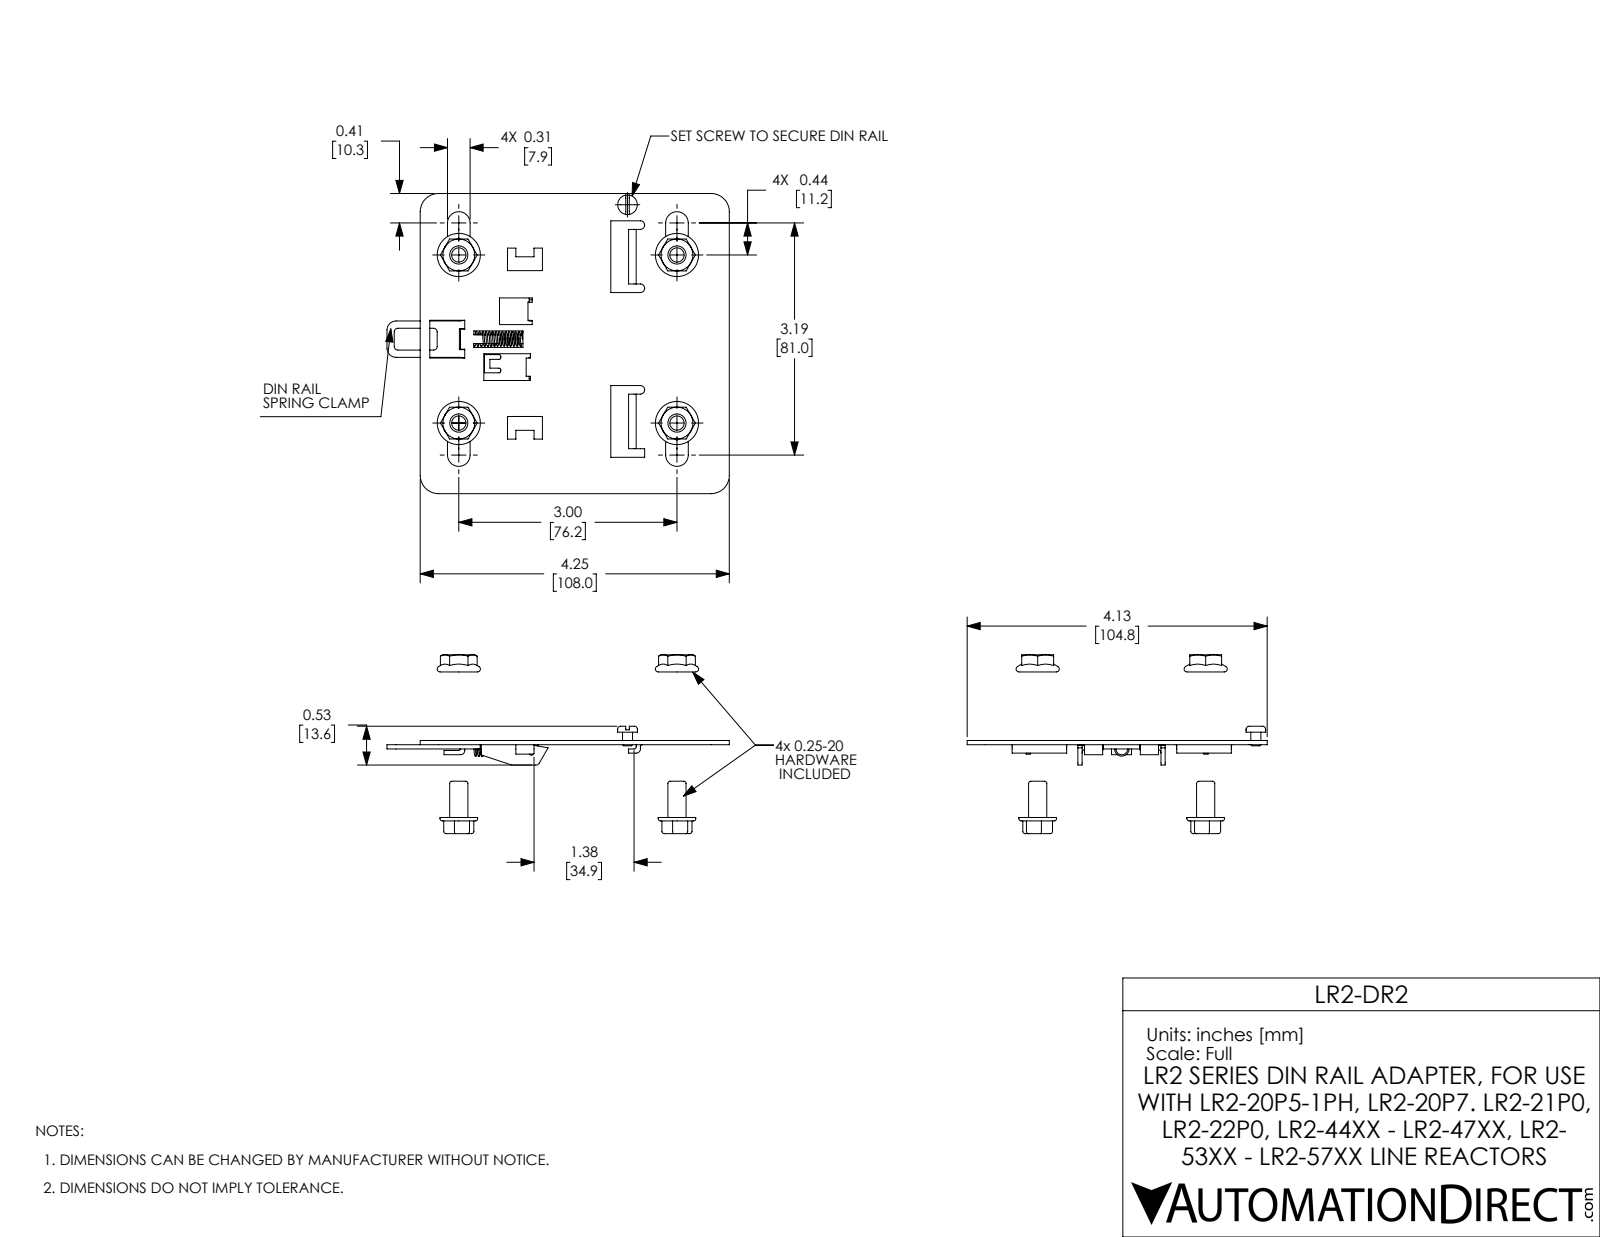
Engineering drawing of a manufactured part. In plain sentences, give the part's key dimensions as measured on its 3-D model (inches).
The part is named "DR-02". Its 3-D file was written by "SolidWorks 2017 (AUTOMOTIVE_DESIGN)". It is 12 solids with 448 faces: 236 planar, 126 cylindrical and 86 other. Overall it measures 4.707 by 4.125 by 2.458 inches. Its volume is 1.366 cubic inches and its surface area 45.83 square inches. Round holes: 4 of diameter 0.196, 1 of diameter 0.104. Round bosses or shafts: 4 of diameter 0.517, 4 of diameter 0.25, 1 of diameter 0.27, 1 of diameter 0.138. Partial cylindrical surfaces (rounded edges, fillets, slot ends): 24 of radius 0.03, 20 of radius 0.058, 13 of radius 0.029, 8 of radius 0.155, 4 of radius 0.025, 4 of radius 0.05, 4 of radius 0.116, 4 of radius 0.25. The main face-to-face distances are 0.058, 0.058, 1, 0.116, 0.942, 0.942, 1.058, 2, 1.058, 2.236. The hole center spacings are 2.31, 3, 3.786, 0.969, 2.42, 3.076, 3.793.
